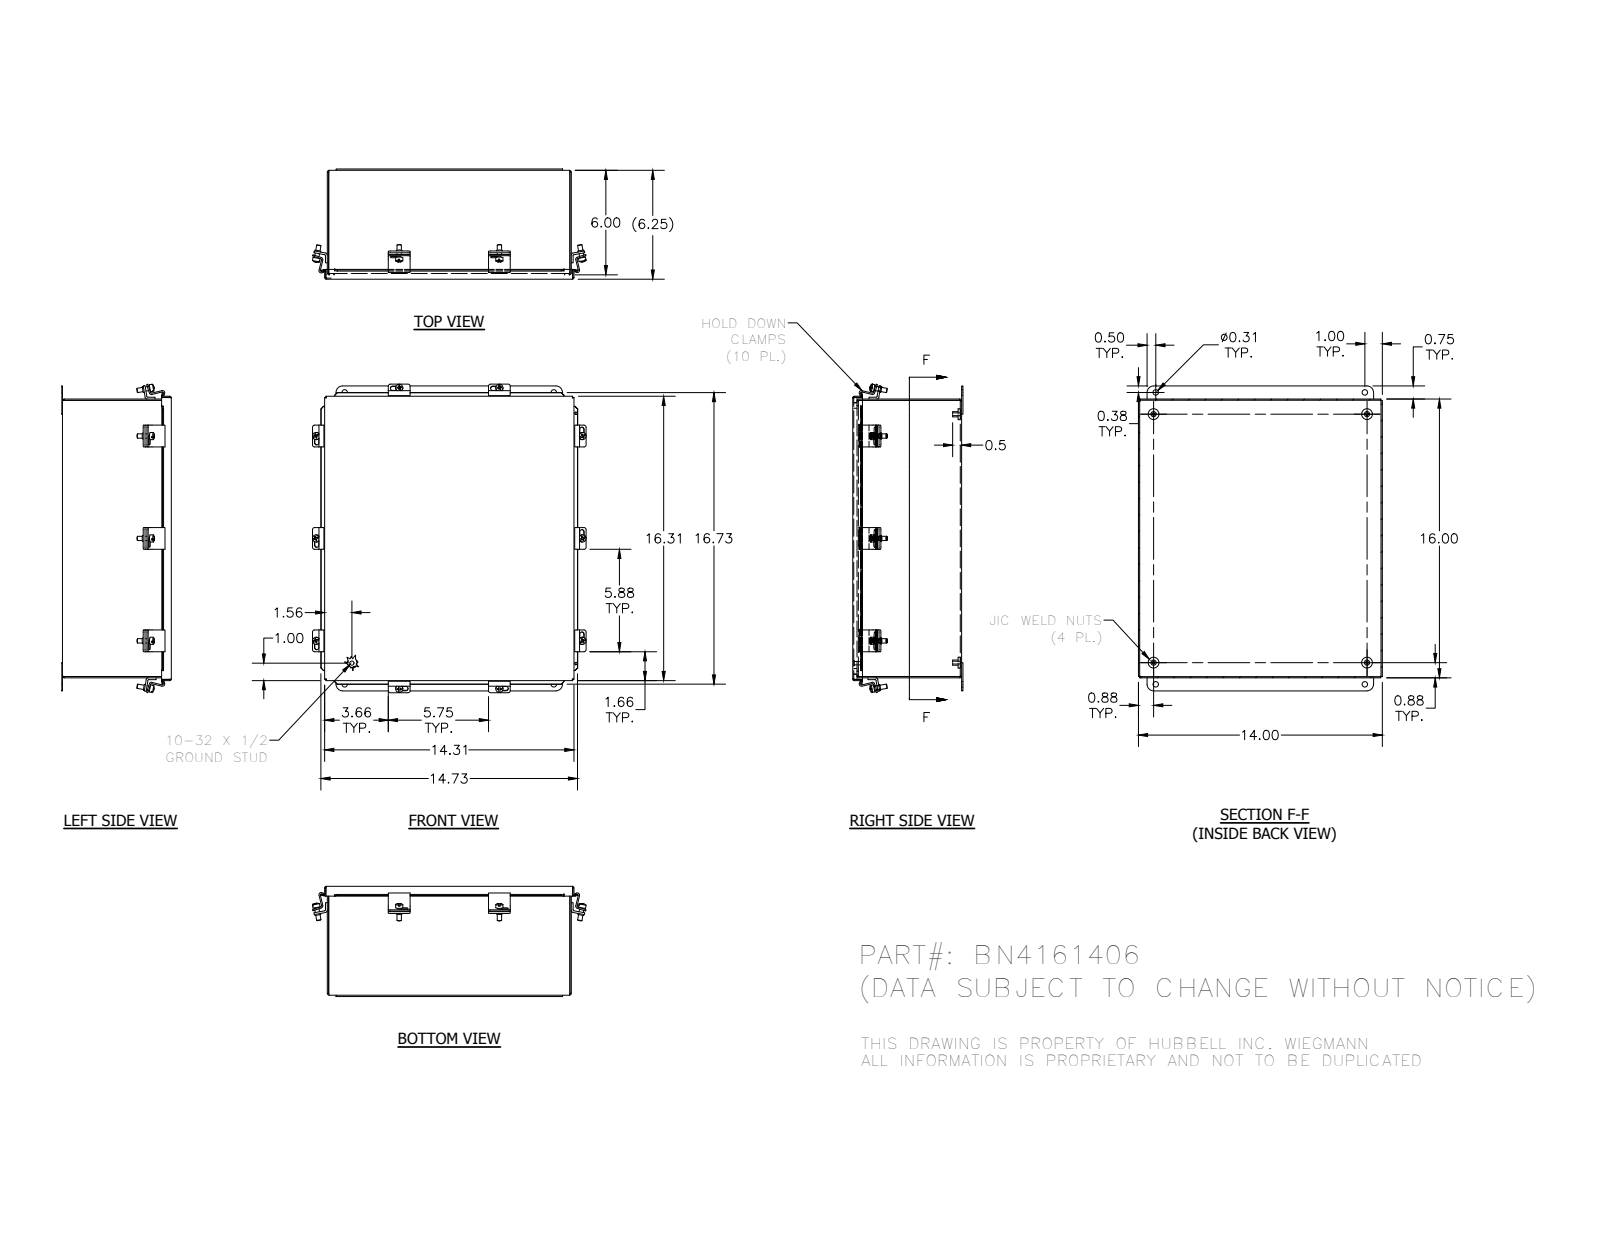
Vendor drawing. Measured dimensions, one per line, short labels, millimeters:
name: 372135_1; 3486_1; BN4161406BKP_1; C1001_1 (+6 more)
written by: SolidWorks 2014 (AUTOMOTIVE_DESIGN)
unit: mm
bodies: 41 solids, 909 faces (499 planar, 316 cylindrical, 94 other)
size: 449.7 × 398.9 × 160.6
volume: 1 217 000 mm³; area: 1 300 000 mm²
holes: 10× ⌀5, 4× ⌀4, 4× ⌀7.9, 2× ⌀3.5
bosses: 11× ⌀6.4, 10× ⌀10.4, 10× ⌀8.7, 4× ⌀15.9, 4× ⌀7.6, 1× ⌀4.8
rounds: 40× R3.2, 20× R3.4, 16× R0.8, 12× R1.6, 12× R3.2, 8× R2.4, 8× R2.7, 4× R9.5
face distances: 1.9, 157.1, 1.6, 158.8, 155.3, 156.9, 353.7, 404.5, 355.6, 351.8
hole spacings: 31.9, 393.7, 499.8, 149.2, 146.1, 304.8, 309.6, 309.6
